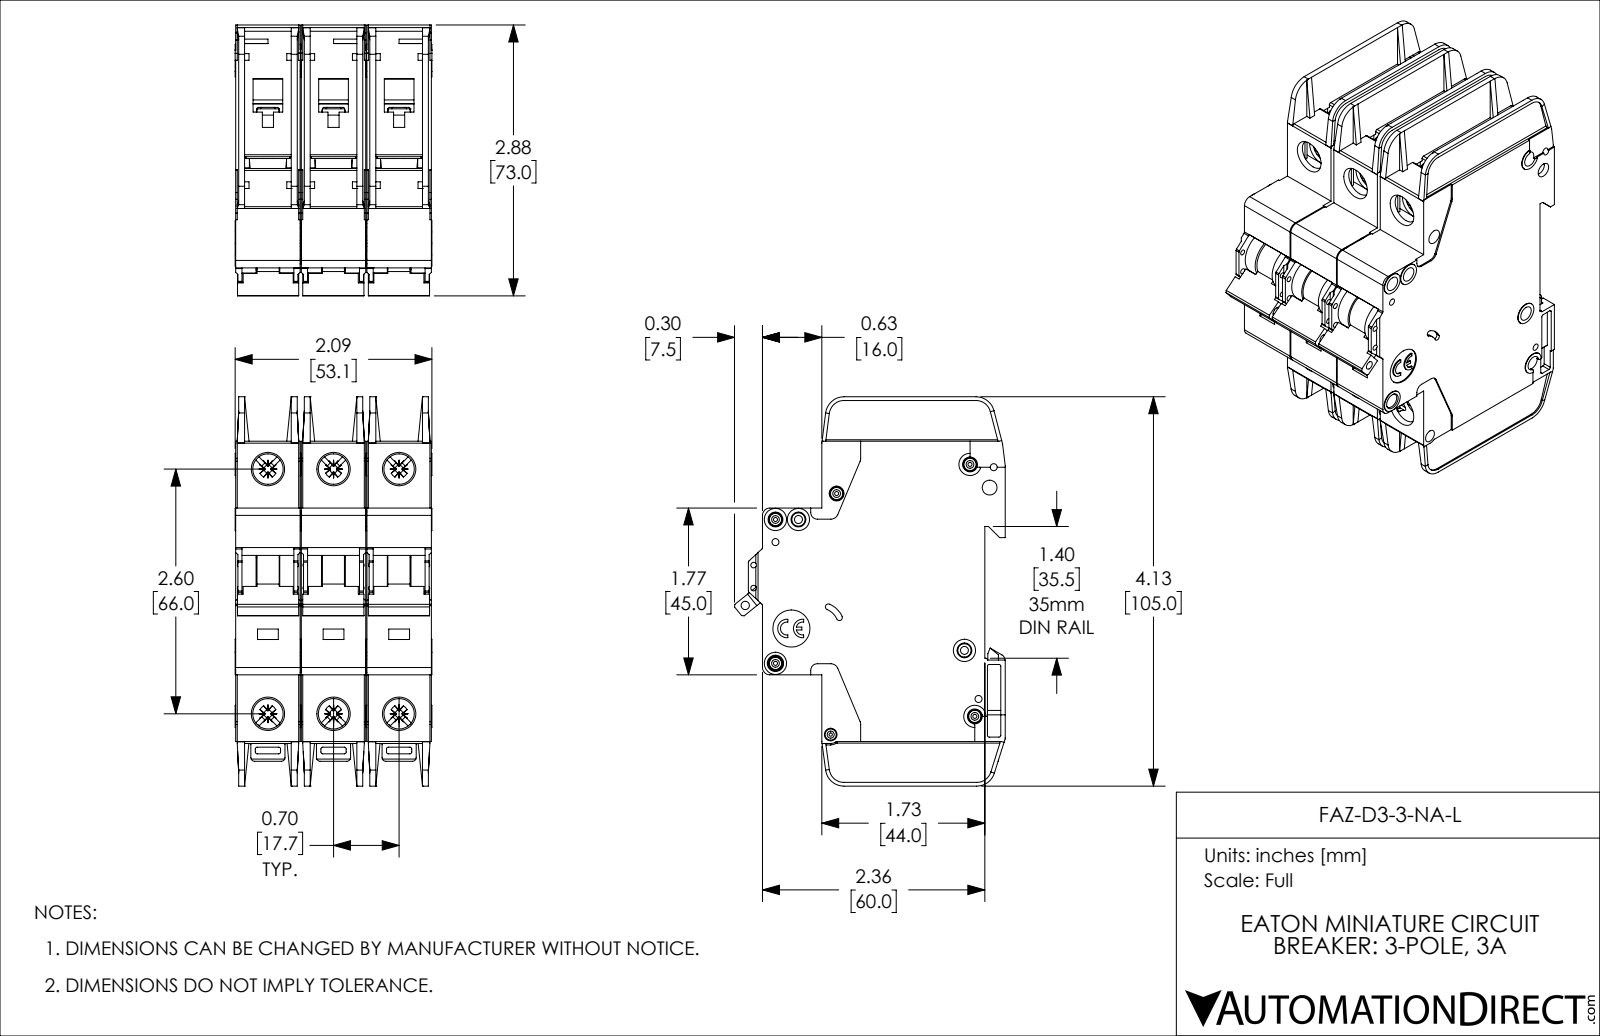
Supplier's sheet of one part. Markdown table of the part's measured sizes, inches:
| quantity | value |
| --- | --- |
| part name | FAZ-D3-3-NA-L |
| STEP written by | SolidWorks 2019 (AUTOMOTIVE_DESIGN) |
| units | inches |
| bodies | 3 solids, 3381 faces (2013 planar, 1071 cylindrical, 297 other) |
| overall size | 4.134 × 2.876 × 2.091 |
| volume | 14.05 in³ |
| surface area | 123 in² |
| round holes (diameter × count) | 0.157 × 8, 0.323 × 6, 0.043 × 5, 0.075 × 4, 0.059 × 2, 0.085 × 2, 0.035 × 1, 0.089 × 1, 0.098 × 1, 0.134 × 1, 0.394 × 1 |
| round bosses / shafts (diameter × count) | 0.13 × 5, 0.236 × 4, 0.118 × 4, 0.098 × 3 |
| partial cylindrical surfaces (radius × count) | 0.02 × 72, 0.016 × 30, 0.039 × 18, 0.043 × 12, 0.079 × 12, 0.008 × 6, 0.01 × 6, 0.028 × 6 |
| main face-to-face distances | 0.697, 0.047, 1.394, 0.685, 0.591, 1.382, 0.744, 0.65, 0.106, 0.094 |
| hole center spacings | 0.697, 2.69, 2.598, 0.244, 0.537, 0.87, 1.394, 2.948 |
